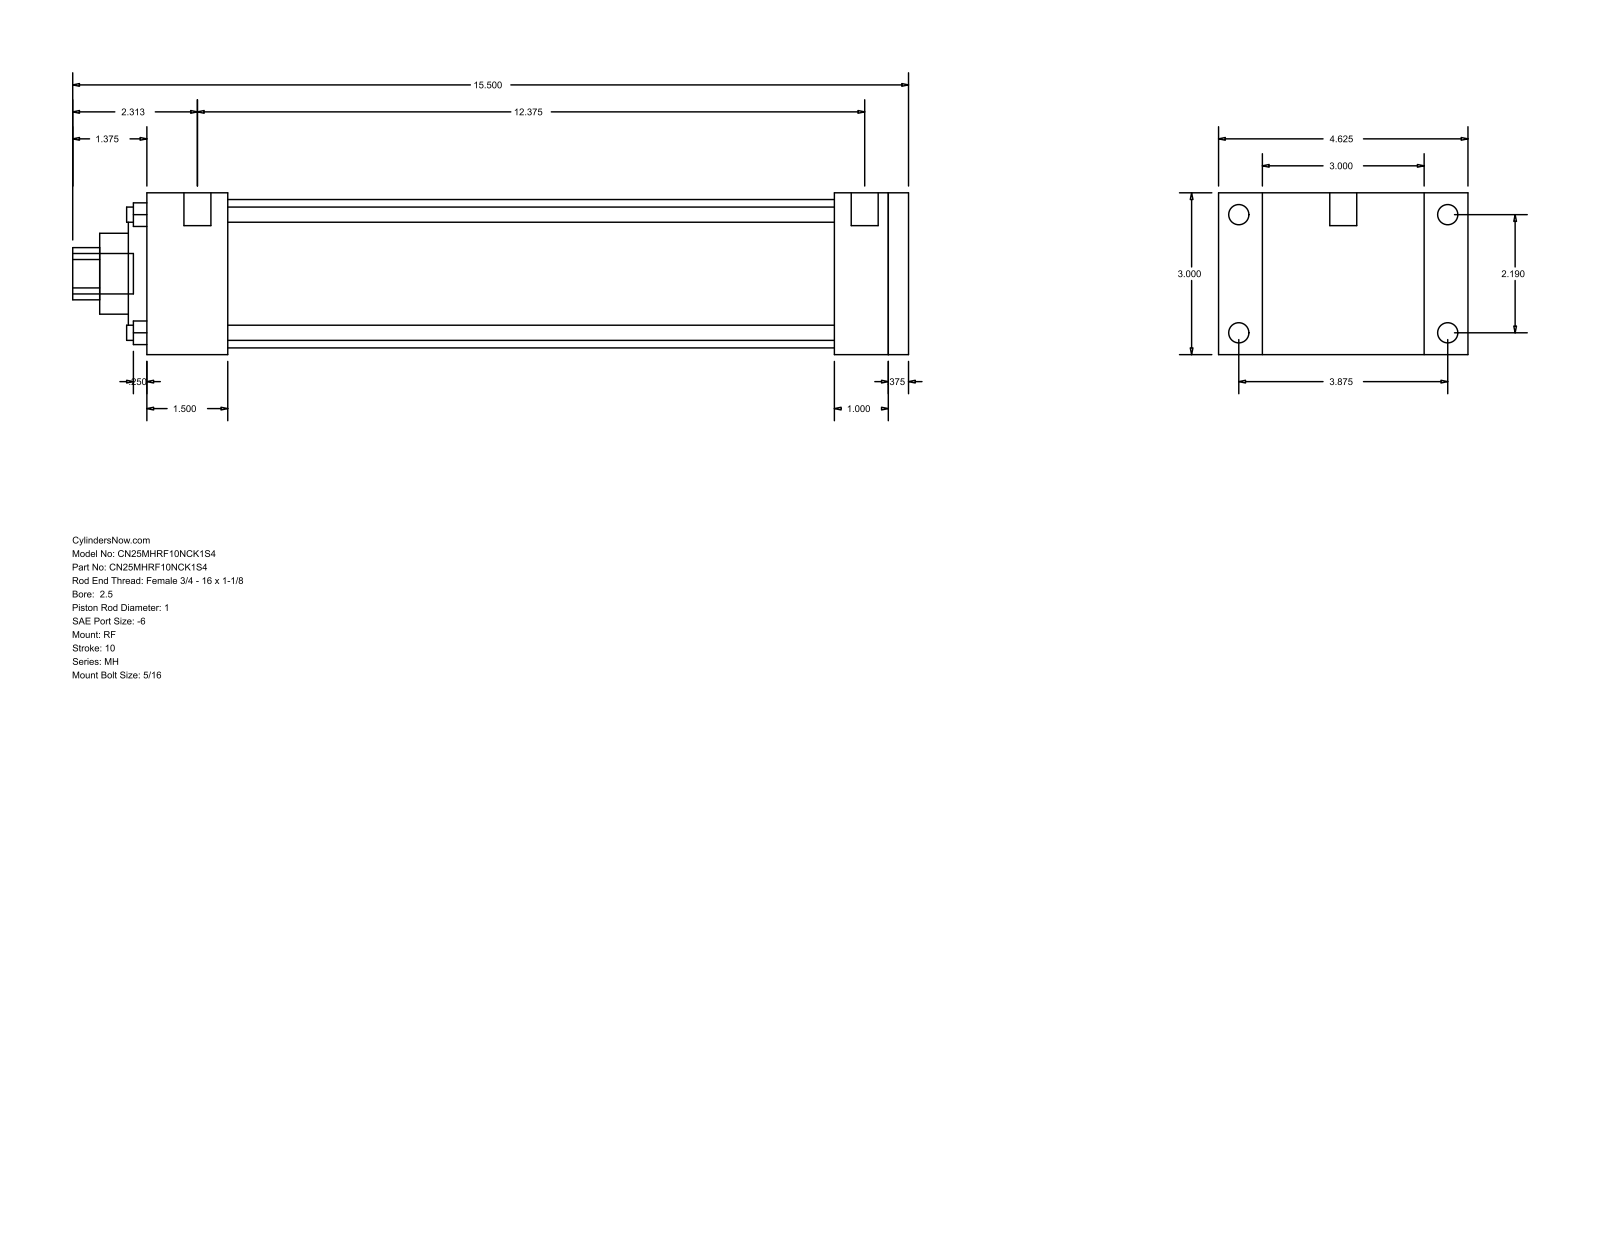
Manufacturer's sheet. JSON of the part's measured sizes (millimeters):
{"part_name": "MH_RF__0250_1", "step_written_by": "GSSL Pune (CONFIG_CONTROL_DESIGN)", "units": "millimeters", "bodies": {"solids": 0, "faces": 94, "planar": 65, "cylindrical": 29, "other": 0}, "overall_size": [393.7, 117.47, 76.2], "round_holes": [[7.14, 4], [25.4, 1], [38.1, 1], [60.33, 1], [69.85, 1]], "round_bosses_or_shafts": [[9.53, 4], [5.56, 4], [12.7, 2], [19.05, 1]], "partial_cylinders_radius": [[12.29, 1]], "face_to_face_distances": [76.2, 9.52, 358.78, 349.26, 323.85, 25.41, 34.93, 38.11, 285.74, 311.15], "hole_center_spacings": [39.33, 55.62, 78.66]}
